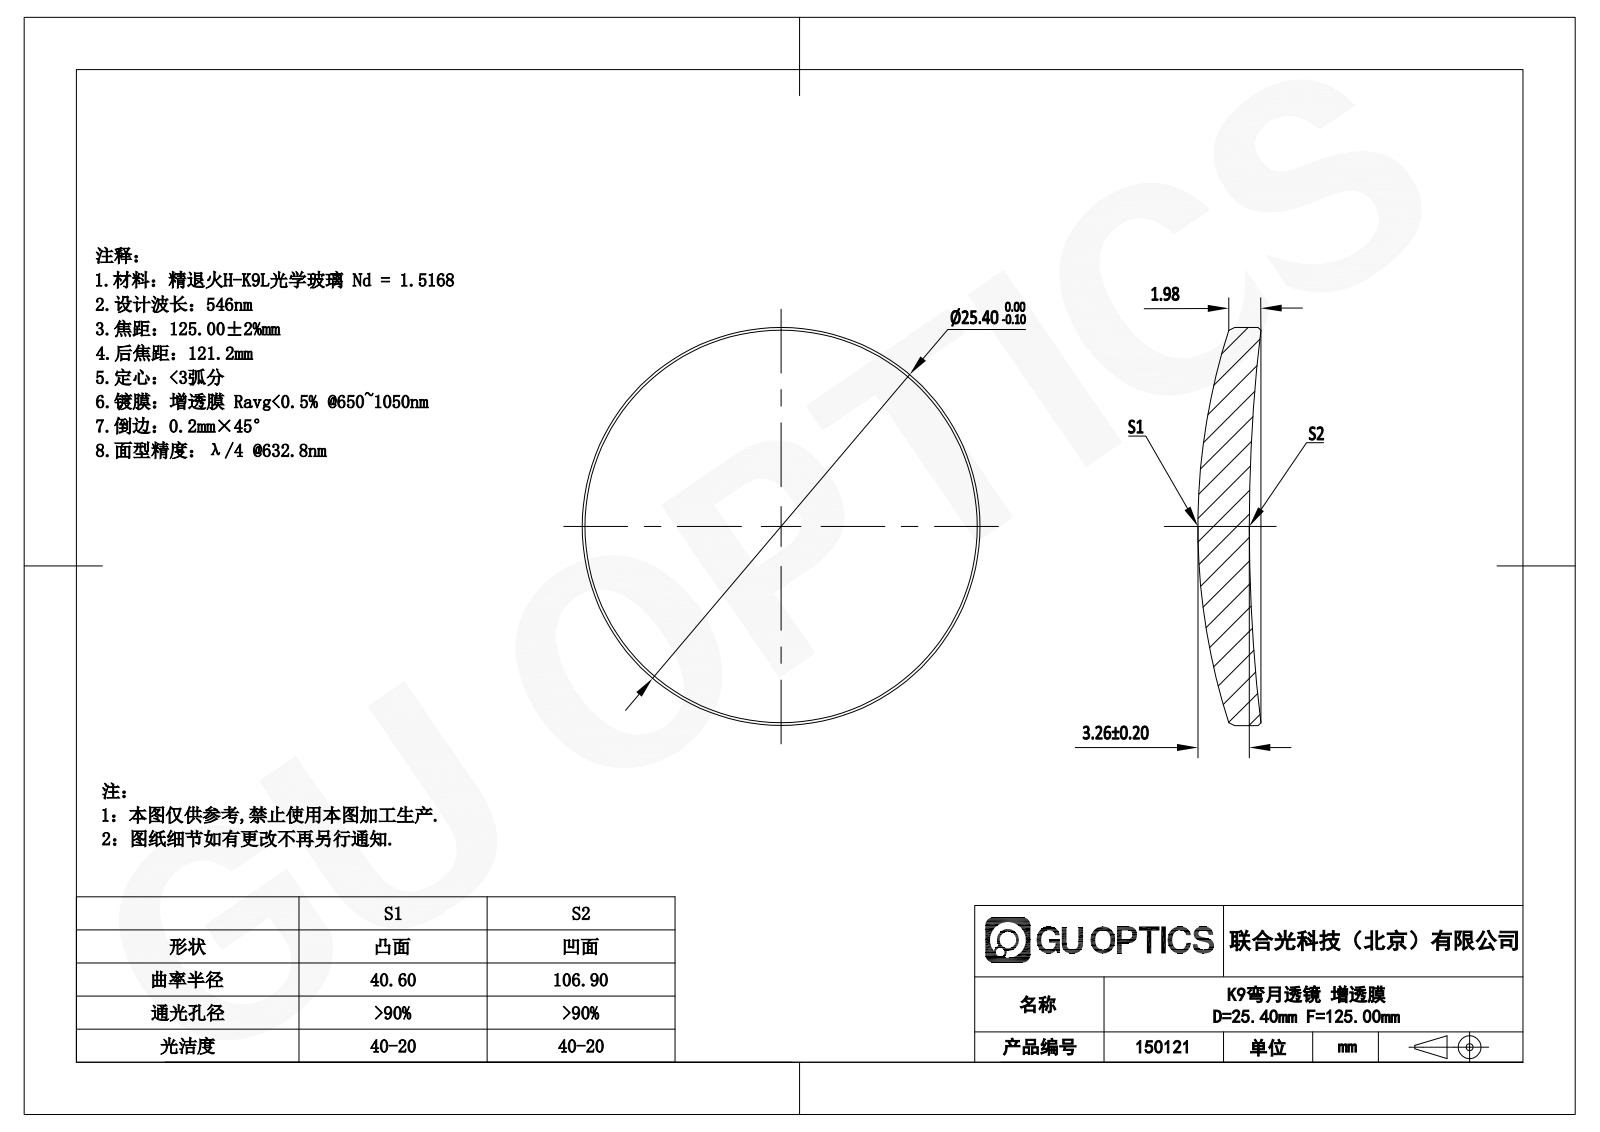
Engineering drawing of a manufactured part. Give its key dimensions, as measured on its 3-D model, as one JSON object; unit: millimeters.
{"part_name": "GLM1-025B-125-NIR", "step_written_by": "SolidWorks 2022 (AUTOMOTIVE_DESIGN)", "units": "millimeters", "bodies": {"solids": 1, "faces": 10, "planar": 0, "cylindrical": 2, "other": 8}, "overall_size": [25.4, 25.4, 4.02], "volume_mm3": 1338, "surface_area_mm2": 1170, "round_bosses_or_shafts": [[25.4, 1]]}
